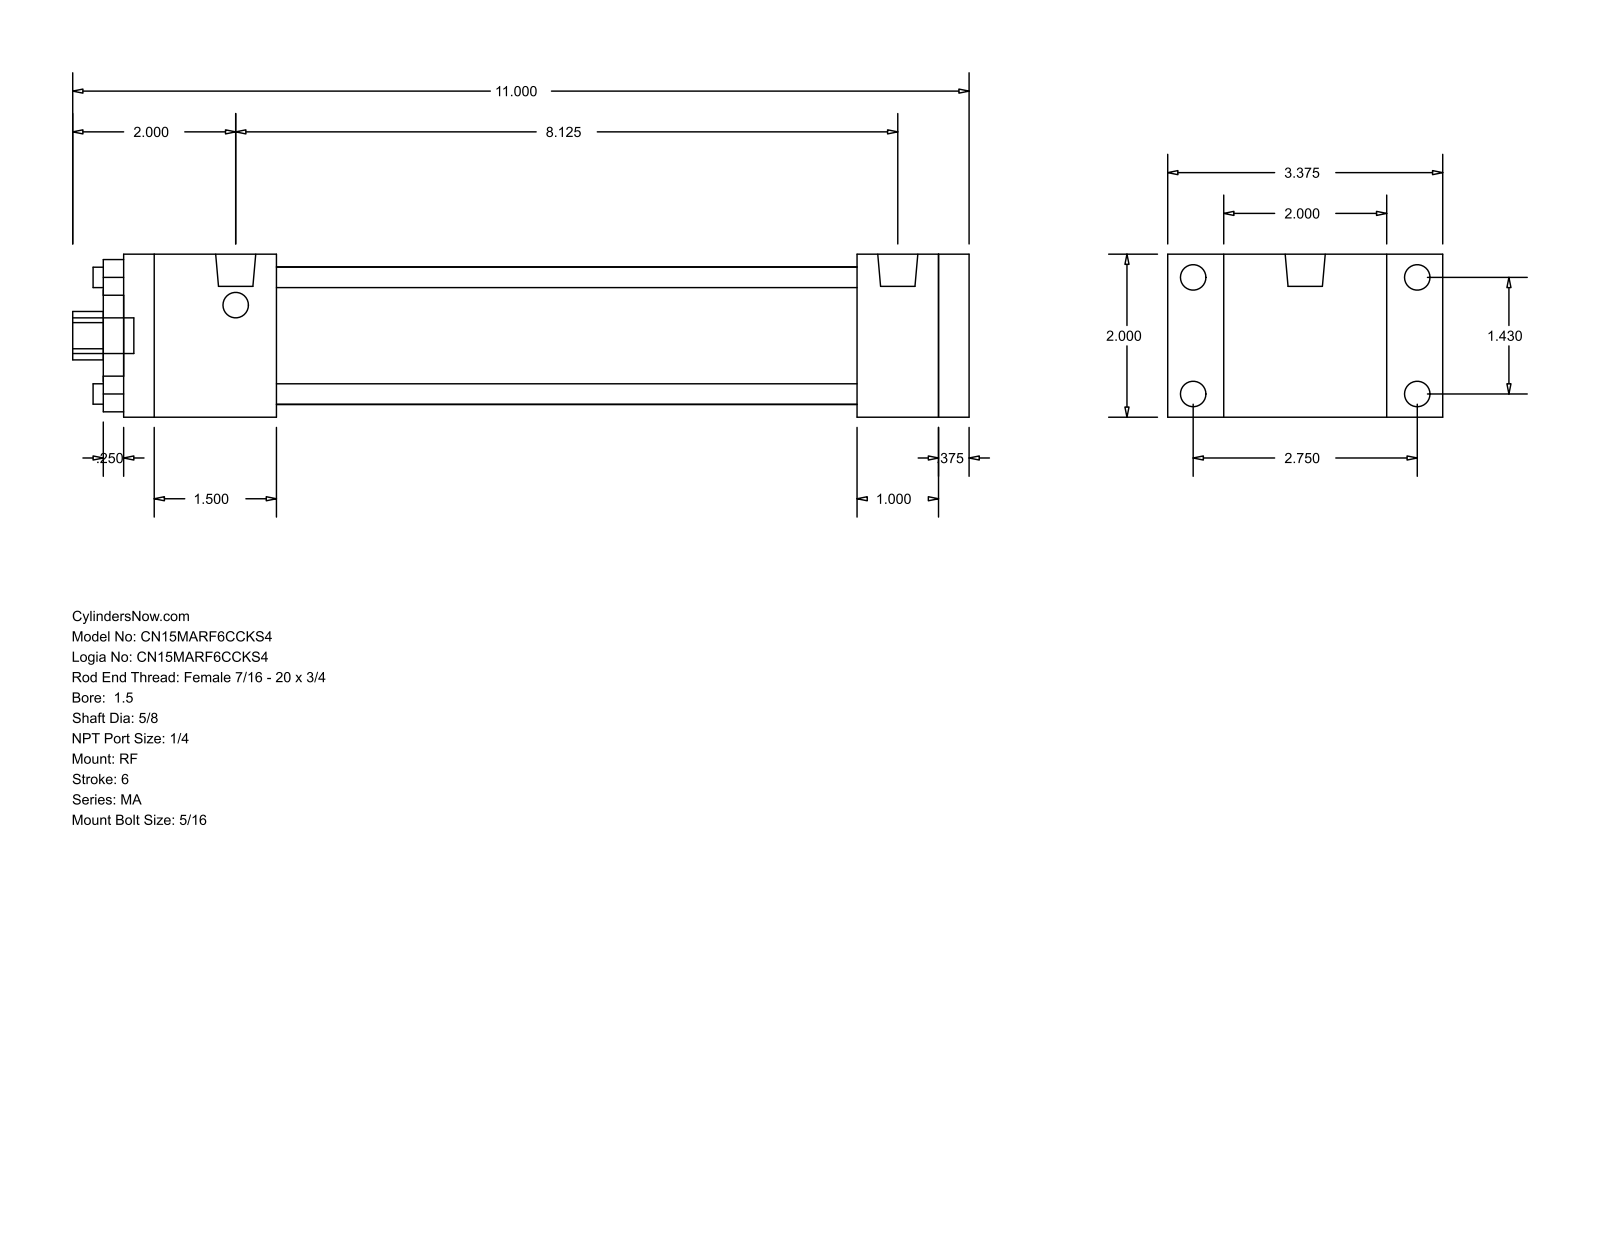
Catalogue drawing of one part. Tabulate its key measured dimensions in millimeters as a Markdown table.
| quantity | value |
| --- | --- |
| part name | MA_RF__0150_0.625 |
| STEP written by | GSSL Pune (CONFIG_CONTROL_DESIGN) |
| units | millimeters |
| bodies | 0 solids, 92 faces (64 planar, 28 cylindrical, 0 other) |
| overall size | 279.4 × 85.72 × 50.8 |
| round holes (diameter × count) | 6.35 × 4, 15.88 × 1, 28.57 × 1, 42.93 × 1 |
| round bosses / shafts (diameter × count) | 7.94 × 8, 12.49 × 2, 11.11 × 1 |
| partial cylindrical surfaces (radius × count) | 7.54 × 1 |
| main face-to-face distances | 50.8, 9.52, 254, 263.52, 228.59, 25.41, 34.93, 47.62, 180.97, 206.38 |
| hole center spacings | 25.68, 36.32, 51.36 |
